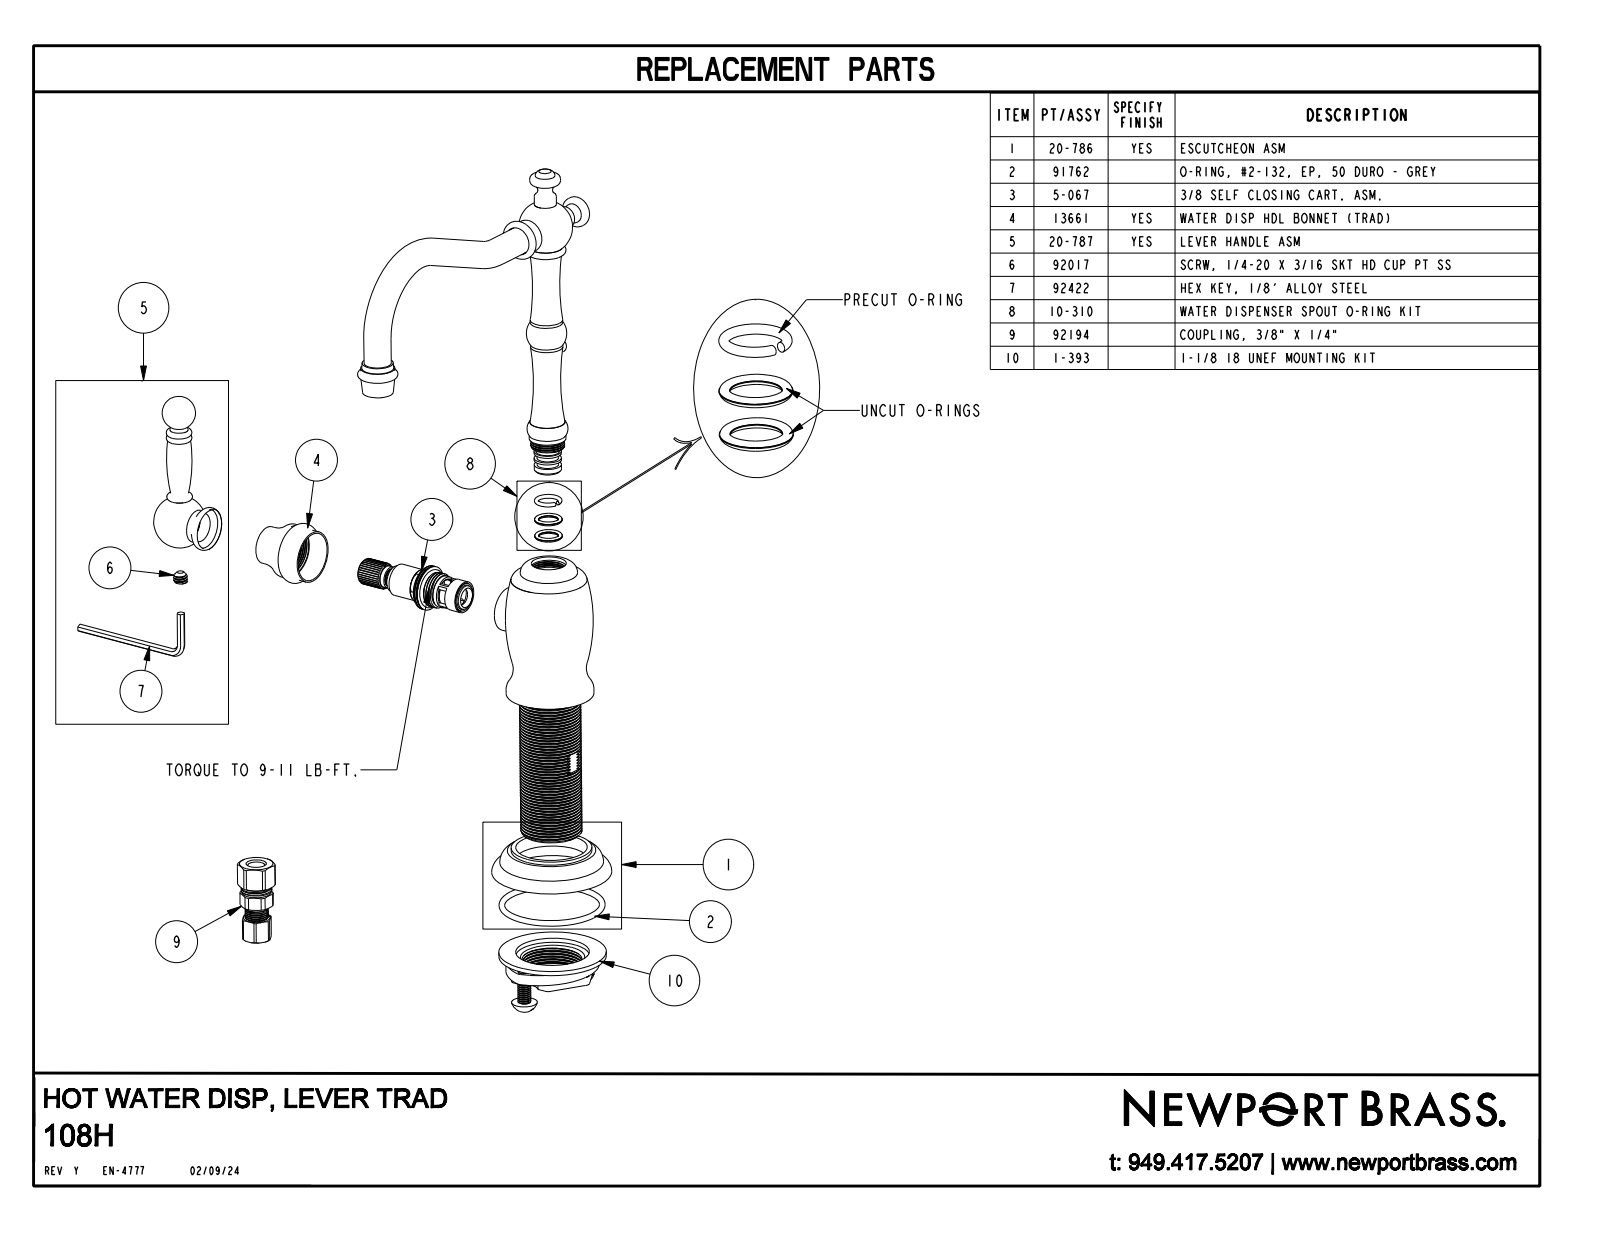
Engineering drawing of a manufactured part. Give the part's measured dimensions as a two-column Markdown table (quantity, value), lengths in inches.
| quantity | value |
| --- | --- |
| part name | 108H |
| STEP written by | CREO PARAMETRIC BY PTC INC, 2018400 (CONFIG_CONTROL_DESIGN) |
| units | inches |
| bodies | 1 solid, 160 faces (20 planar, 42 cylindrical, 98 other) |
| overall size | 8.252 × 6.653 × 3.828 |
| volume | 10.05 in³ |
| surface area | 52.66 in² |
| round holes (diameter × count) | 1 × 1 |
| round bosses / shafts (diameter × count) | 0.5 × 3, 0.6 × 2, 0.562 × 2, 0.405 × 2, 0.357 × 2, 1.61 × 1, 1.48 × 1, 0.95 × 1 |
| main face-to-face distances | 0.425, 0.43, 5.825, 5.4, 5.395, 0.03, 0.156, 0.243, 0.087, 1 |
